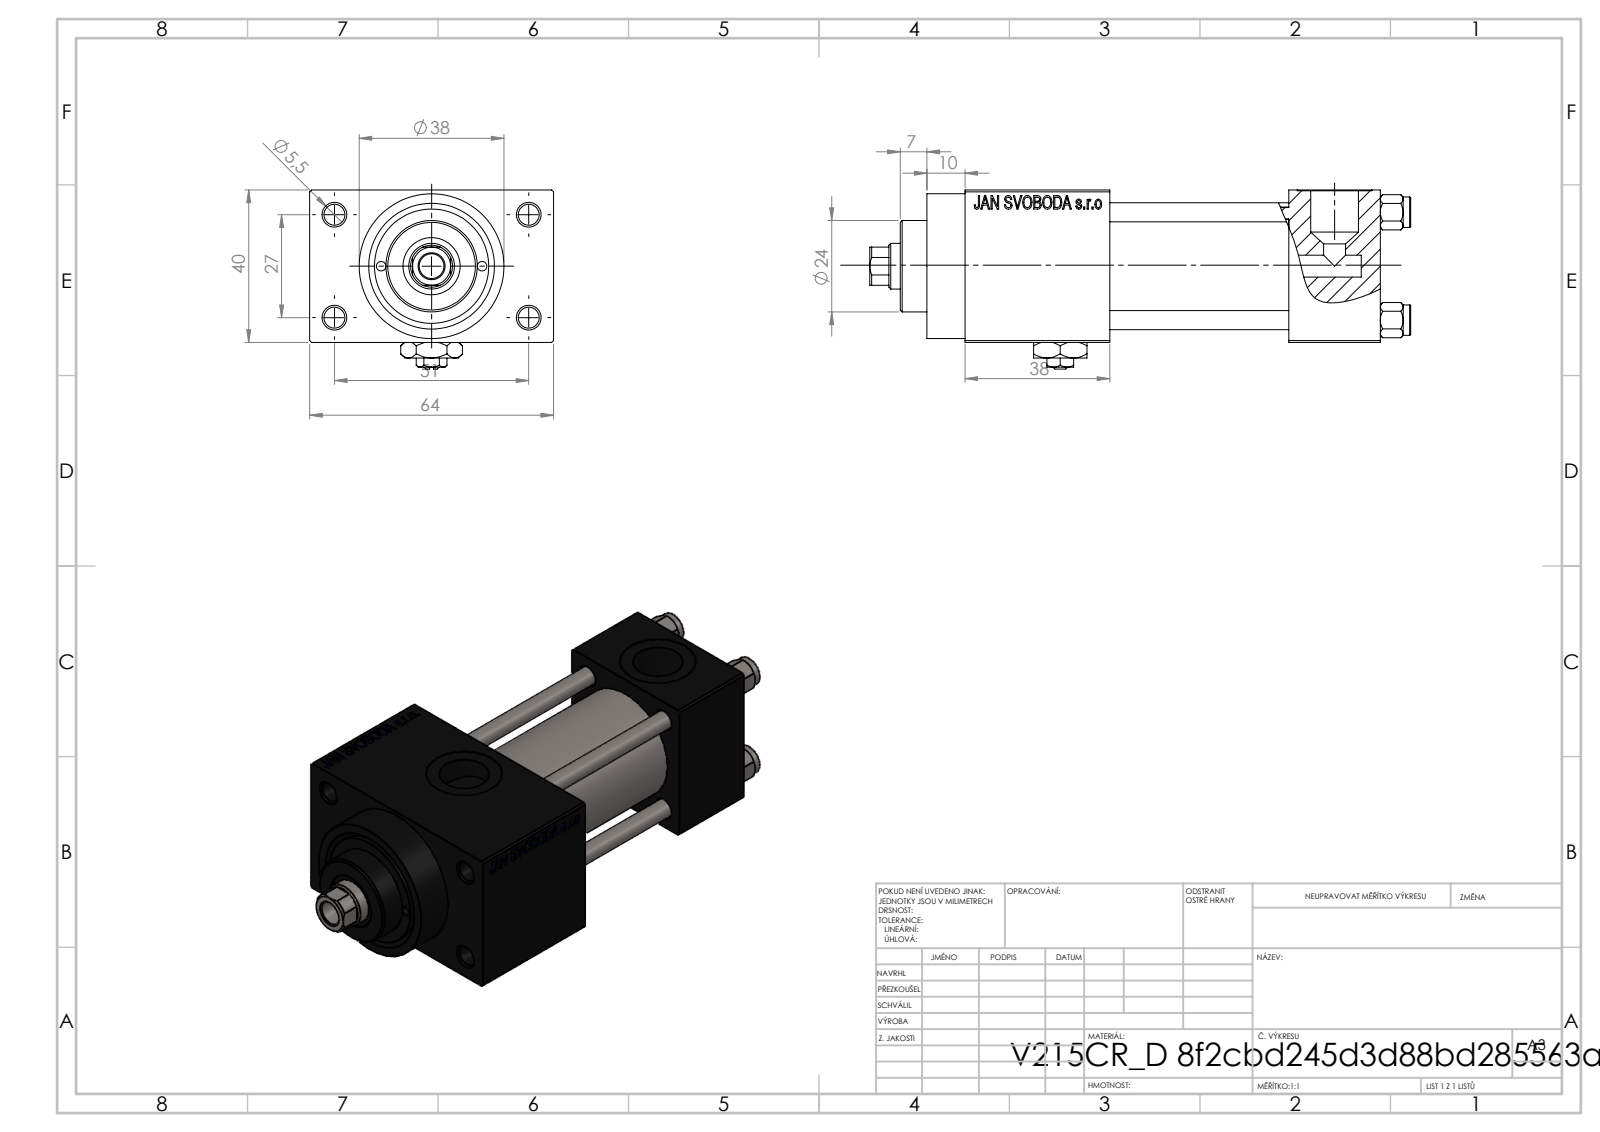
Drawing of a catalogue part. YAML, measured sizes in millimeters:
part_name: "Zatka_pro_OIL_PORT; V215CR_D_Body; NUT_M5_D; V215_VC_A (+2 more)"
step_written_by: "SolidWorks 2019 (CONFIG_CONTROL_DESIGN)"
units: millimeters
bodies: {solids: 12, faces: 1158, planar: 521, cylindrical: 97, other: 540}
overall_size: [142, 64, 47]
volume: 175130
surface_area: 62225
round_holes:
  - {diameter: 5, count: 4}
  - {diameter: 5.5, count: 4}
  - {diameter: 20, count: 3}
  - {diameter: 2.5, count: 2}
  - {diameter: 7, count: 2}
  - {diameter: 13.16, count: 2}
  - {diameter: 6.5, count: 1}
  - {diameter: 12, count: 1}
  - {diameter: 15, count: 1}
  - {diameter: 25, count: 1}
  - {diameter: 30, count: 1}
round_bosses_or_shafts:
  - {diameter: 8, count: 4}
  - {diameter: 38, count: 1}
  - {diameter: 31, count: 1}
  - {diameter: 24, count: 1}
partial_cylinders:
  - {radius: 5.5, count: 1}
face_to_face_distances: [40, 12, 52, 47, 24, 71, 64, 38, 85, 109]
hole_center_spacings: [11.37, 14.18, 18.23, 20.01, 28.3, 28.85, 29.89, 30.84]
